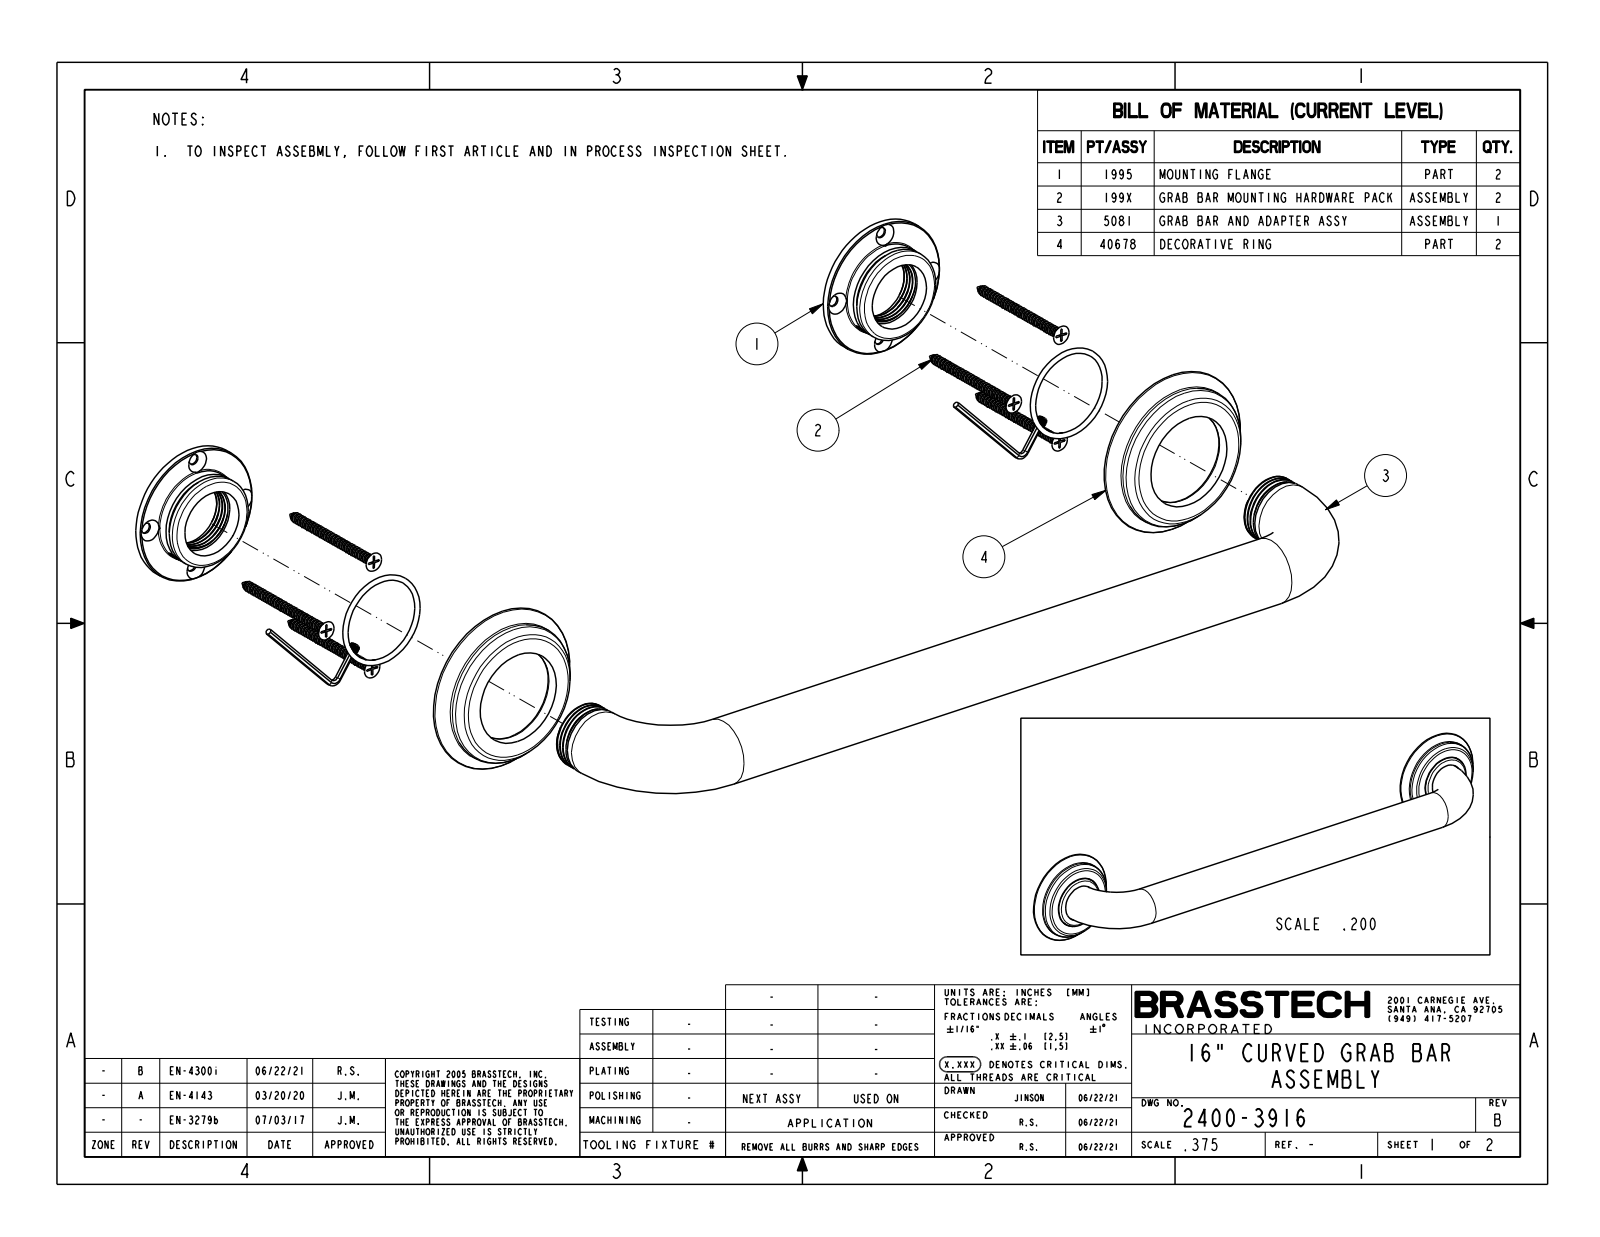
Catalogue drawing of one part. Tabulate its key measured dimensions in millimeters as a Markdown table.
| quantity | value |
| --- | --- |
| part name | 2400-3916 |
| STEP written by | CREO PARAMETRIC BY PTC INC, 2018400 (CONFIG_CONTROL_DESIGN) |
| units | millimeters |
| bodies | 1 solid, 44 faces (6 planar, 6 cylindrical, 32 other) |
| overall size | 486.5 × 80.1 × 69.9 |
| volume | 465 400 mm³ |
| surface area | 66 840 mm² |
| round bosses / shafts (diameter × count) | 44.5 × 2, 31.8 × 1 |
| main face-to-face distances | 13.3, 15.2, 1.9 |
